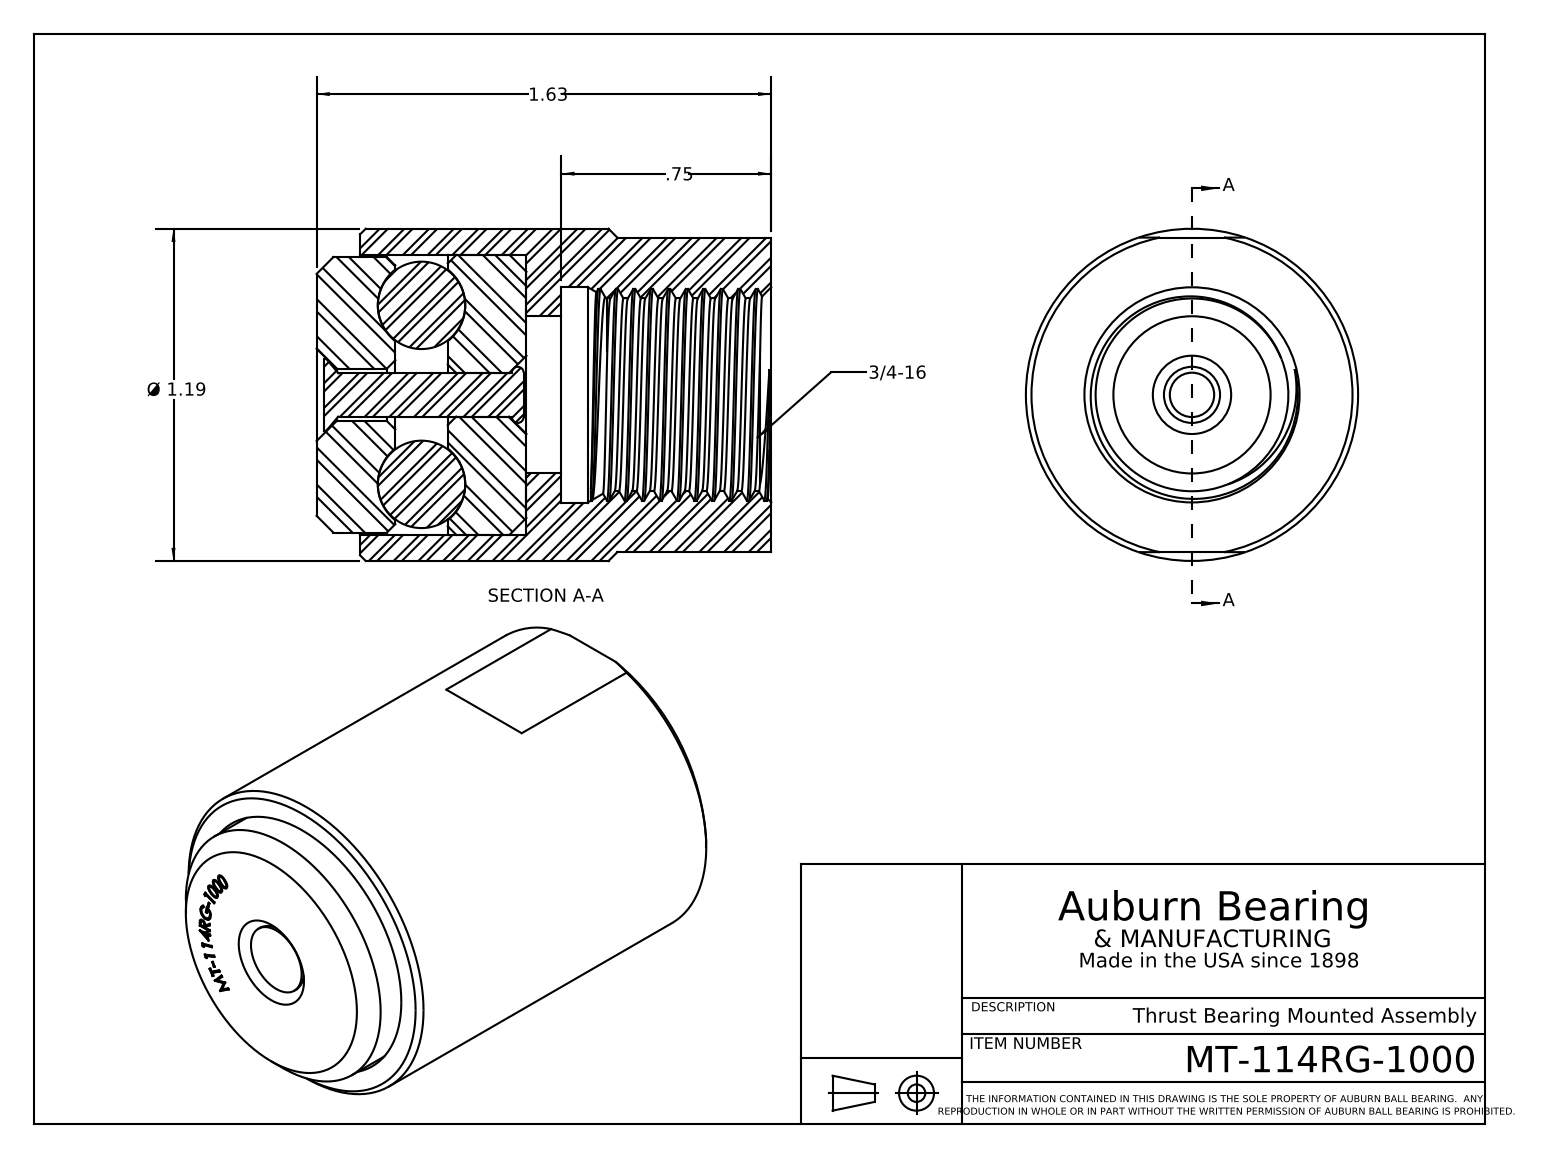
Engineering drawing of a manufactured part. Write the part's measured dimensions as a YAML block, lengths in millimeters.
part_name: "MT-114RG-1000"
step_written_by: "SolidWorks 2020 (CONFIG_CONTROL_DESIGN)"
units: millimeters
bodies: {solids: 10, faces: 243, planar: 111, cylindrical: 41, other: 91}
overall_size: [41.3, 30.2, 30.2]
volume: 20910
surface_area: 12210
round_holes:
  - {diameter: 4, count: 1}
  - {diameter: 4.7, count: 1}
  - {diameter: 14.3, count: 1}
  - {diameter: 17.5, count: 1}
  - {diameter: 19.6, count: 1}
  - {diameter: 25.4, count: 1}
  - {diameter: 25.5, count: 1}
round_bosses_or_shafts:
  - {diameter: 30.2, count: 1}
  - {diameter: 25.4, count: 1}
  - {diameter: 25, count: 1}
  - {diameter: 6.5, count: 1}
face_to_face_distances: [22.2, 19.1, 41.3, 3.9, 15.1, 37.3, 18.3, 3.2, 28.5, 11.9]
